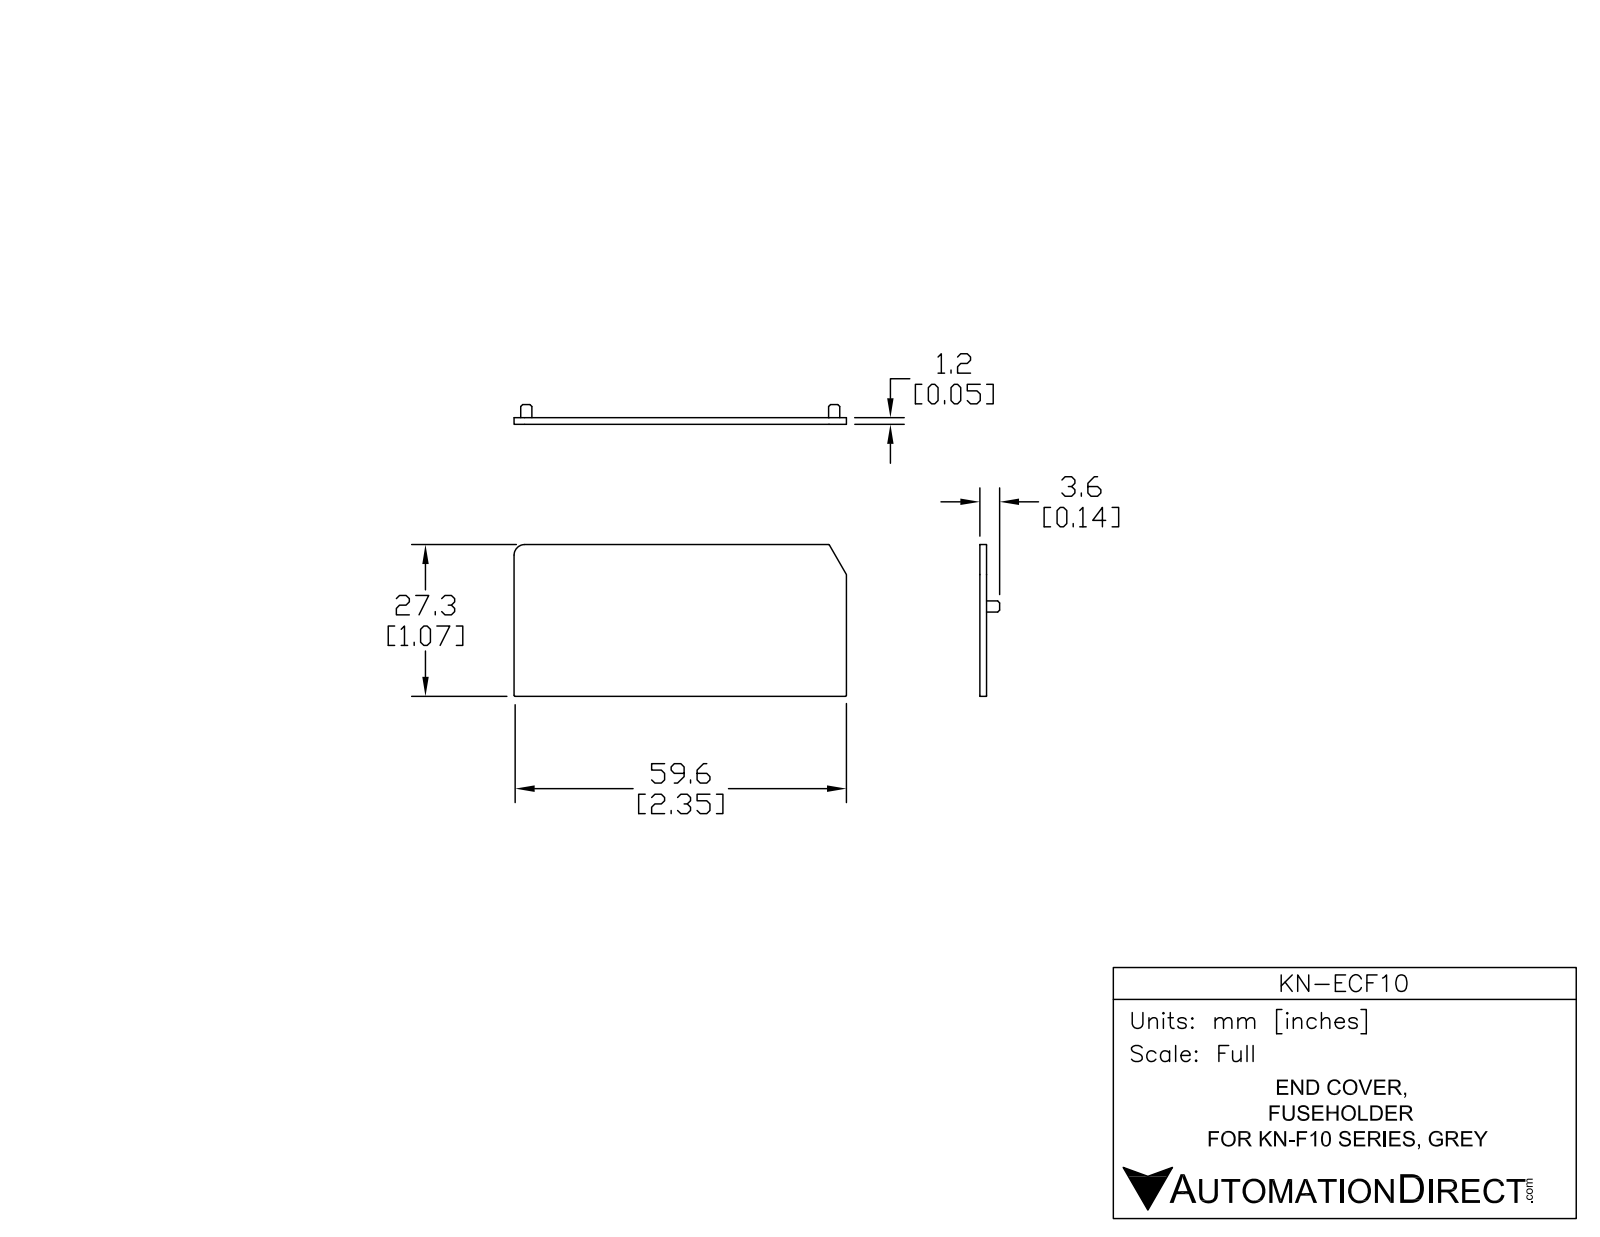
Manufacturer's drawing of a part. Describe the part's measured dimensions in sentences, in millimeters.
The part is named "KN-ECF10". Its 3-D file was written by "SolidWorks 2014 (AUTOMOTIVE_DESIGN)". It is 1 solid with 26 faces: 9 planar, 13 cylindrical and 4 other. Overall it measures 59.8 by 27.3 by 3.55 millimeters. Its volume is 1 956 cubic millimeters and its surface area 3 498 square millimeters. Round holes: 2 of diameter 1.3. Round bosses or shafts: 2 of diameter 2. Partial cylindrical surfaces (rounded edges, fillets, slot ends): 4 of radius 0.2, 1 of radius 1.9. The main face-to-face distances are 1.2, 27.3, 59.8. The hole center spacings are 55.4.
